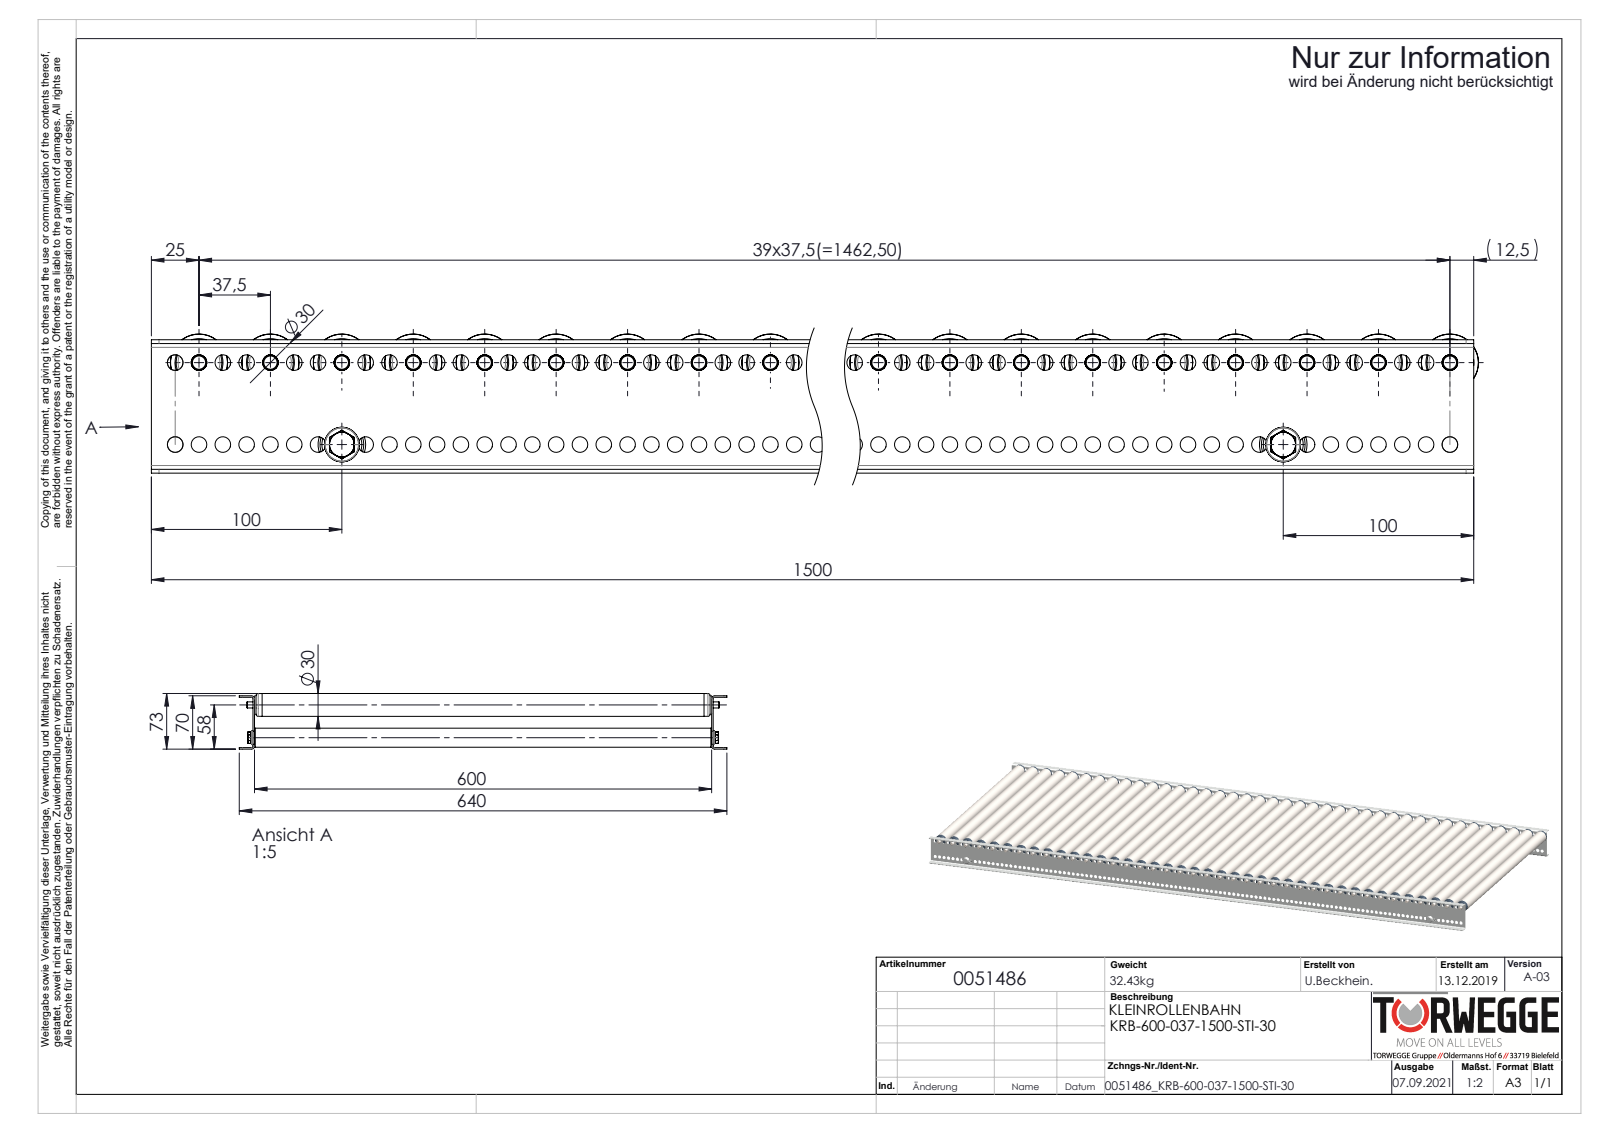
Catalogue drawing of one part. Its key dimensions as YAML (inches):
part_name: "0040250_DRUCK-FEDER-8mm; KUT50-30x1,5-STI-A8-FA_KFG_S100907_KUT50-30x1,5-STI-A8-FA-EL=600; S100994_Sperrzahnschraube_M08x16-8.8-A2K; 0024176_Passscheibe_DIN988_8x14x1 (+6 more)"
step_written_by: "SolidWorks 2020 (AUTOMOTIVE_DESIGN)"
units: inches
bodies: {solids: 252, faces: 10592, planar: 3320, cylindrical: 4208, other: 3064}
overall_size: [59.154, 25.197, 2.874]
volume: 314.8
surface_area: 9531
round_holes:
  - {diameter: 0.323, count: 238}
  - {diameter: 0.315, count: 40}
  - {diameter: 0.319, count: 40}
  - {diameter: 0.913, count: 40}
  - {diameter: 0.992, count: 40}
  - {diameter: 1.063, count: 40}
  - {diameter: 0.268, count: 2}
  - {diameter: 0.827, count: 2}
round_bosses_or_shafts:
  - {diameter: 1.181, count: 40}
  - {diameter: 1.177, count: 40}
  - {diameter: 1.067, count: 40}
  - {diameter: 1.055, count: 40}
  - {diameter: 0.945, count: 40}
  - {diameter: 0.551, count: 40}
  - {diameter: 0.984, count: 2}
  - {diameter: 0.315, count: 2}
partial_cylinders:
  - {radius: 0.199, count: 40}
  - {radius: 0.157, count: 8}
  - {radius: 0.079, count: 4}
face_to_face_distances: [0.079, 23.701, 23.622, 2.677, 23.78, 2.756, 2.598, 0.394, 23.228, 0.787]
hole_center_spacings: [0.492, 0.984, 1.476, 1.969, 2.461, 2.953, 3.445, 3.937]
